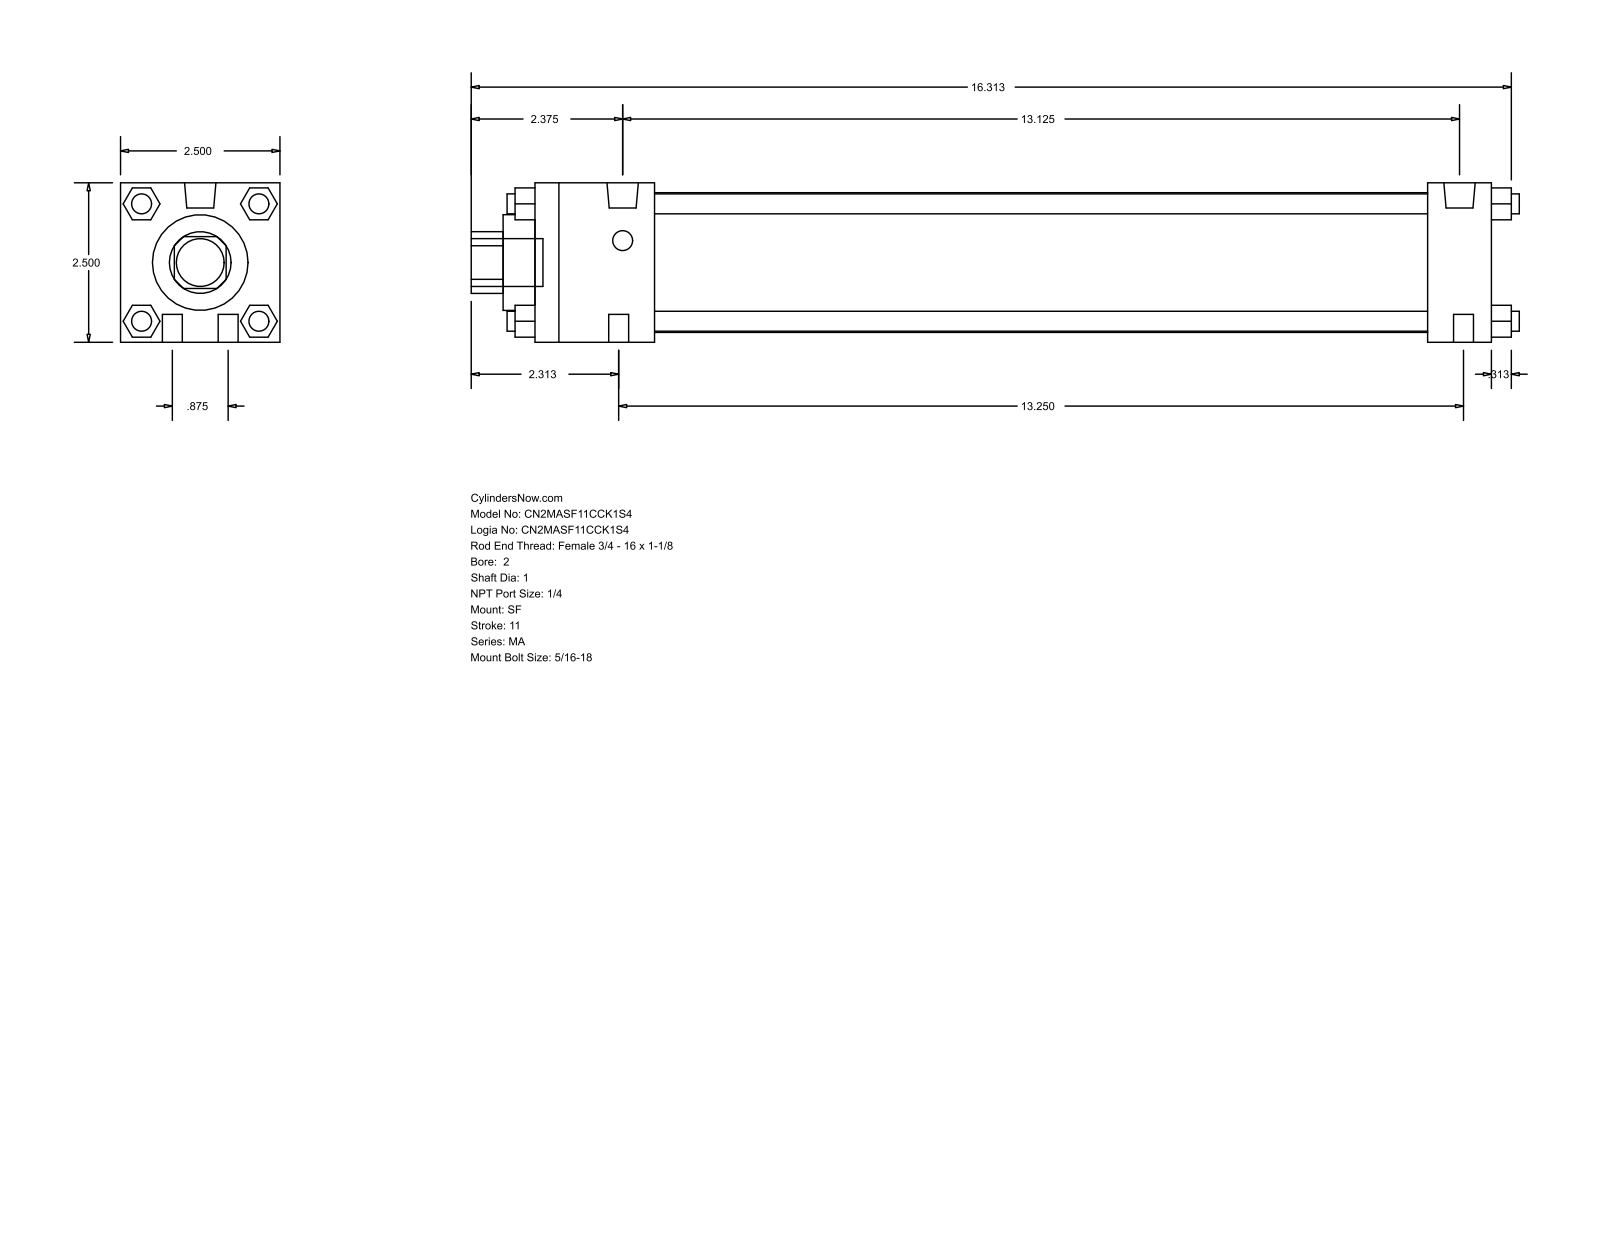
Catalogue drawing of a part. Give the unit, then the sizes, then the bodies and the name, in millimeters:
Units: millimetres
Overall size (bounding box): 417.51 × 63.5 × 63.5
Round holes (diameter × count): ⌀25.4 ×1, ⌀38.1 ×1, ⌀55.63 ×1
Round bosses / shafts (diameter × count): ⌀7.94 ×10, ⌀12.49 ×2, ⌀19.05 ×1
Partial cylindrical surfaces — rounded edges, fillets, slot ends (radius × count): R12.29 ×1
Main face-to-face distances: 63.5, 381, 12.7, 25.4, 355.6, 47.63, 307.97, 333.37, 40.47, 23.37
Bodies: 0 solids, 124 faces (94 planar, 30 cylindrical, 0 other)
Part name (STEP PRODUCT): MA_SF__0200_1
STEP written by: GSSL Pune (CONFIG_CONTROL_DESIGN)
